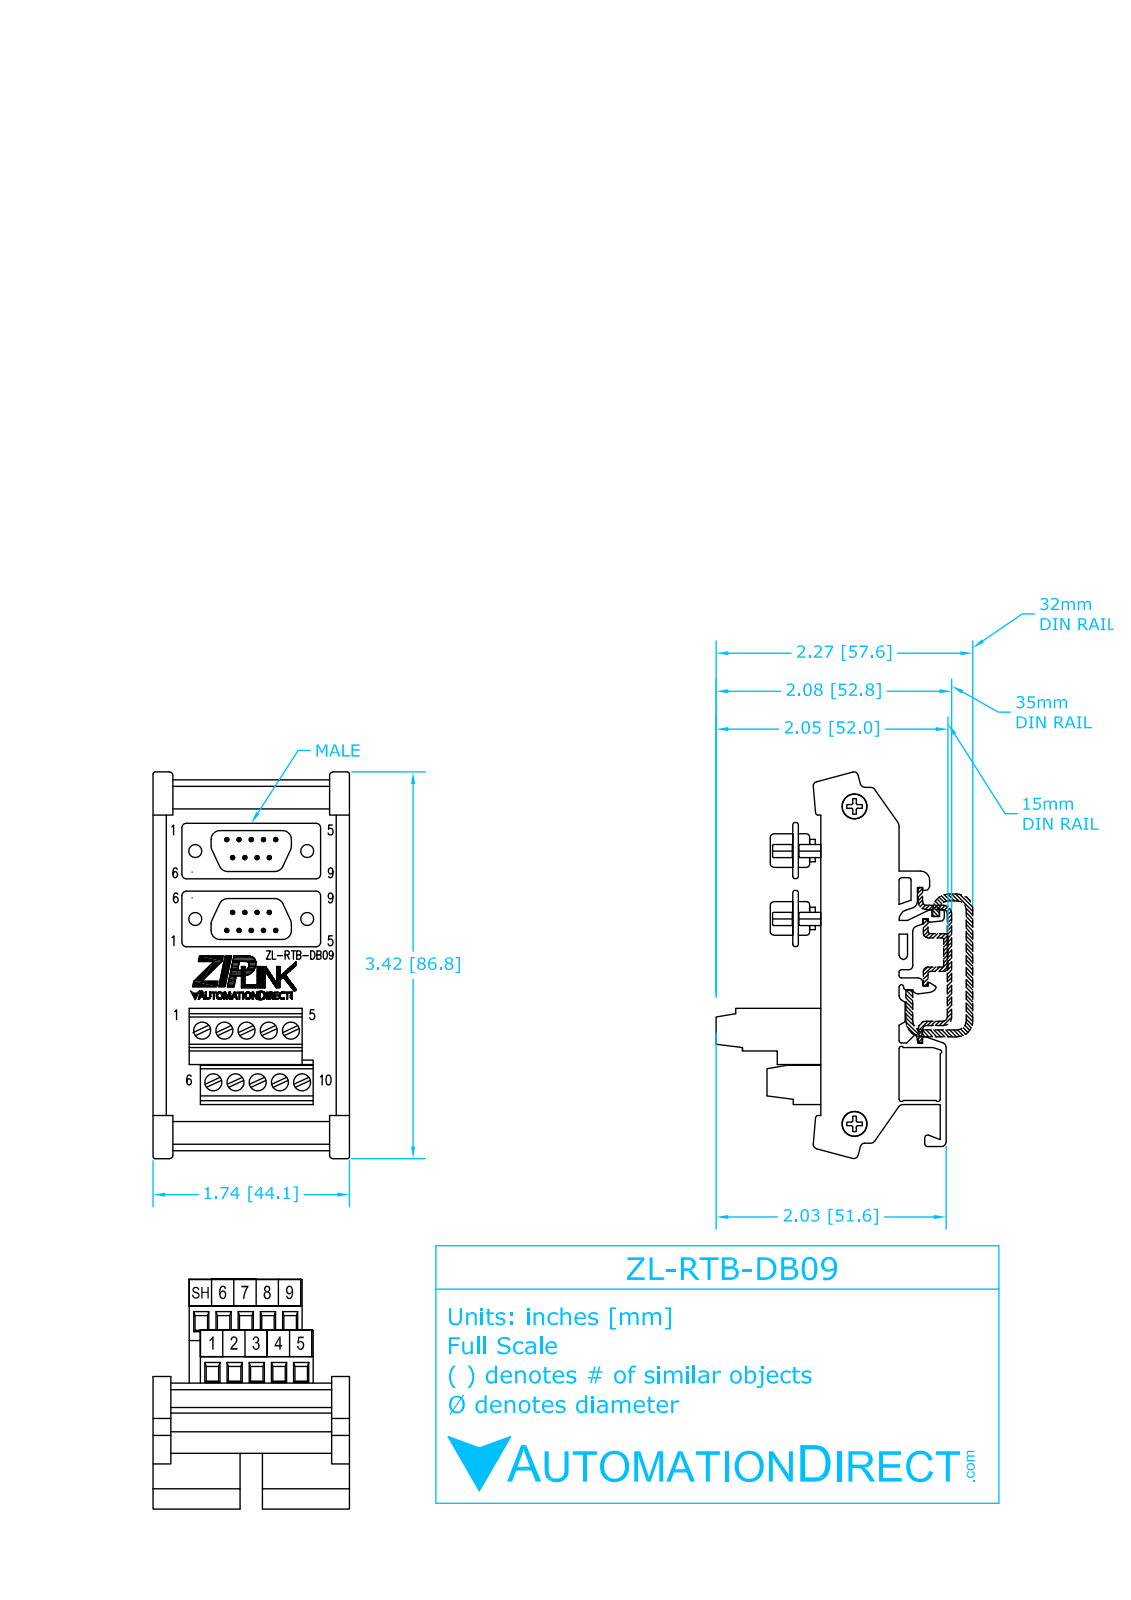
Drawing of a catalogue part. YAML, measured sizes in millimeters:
part_name: "ZL-RTB-DB09"
step_written_by: "SolidWorks 2014 (AUTOMOTIVE_DESIGN)"
units: millimeters
bodies: {solids: 1, faces: 786, planar: 557, cylindrical: 221, other: 8}
overall_size: [86.9, 51.6, 45.6]
volume: 75950
surface_area: 27730
round_holes:
  - {diameter: 3.8, count: 10}
  - {diameter: 1.4, count: 8}
  - {diameter: 2.3, count: 4}
  - {diameter: 5.7, count: 2}
  - {diameter: 1.4, count: 1}
round_bosses_or_shafts:
  - {diameter: 0.9, count: 8}
  - {diameter: 5.2, count: 2}
  - {diameter: 0.9, count: 1}
partial_cylinders:
  - {radius: 0.4, count: 41}
  - {radius: 0.8, count: 10}
  - {radius: 1.5, count: 8}
  - {radius: 2, count: 8}
  - {radius: 2.5, count: 8}
face_to_face_distances: [44.2, 0.8, 27.4, 28.2, 23.6, 0.9, 6.1, 10.7, 16.8, 17.5]
hole_center_spacings: [2.5, 5, 11.4, 3.2, 5.1, 10, 13.4, 3.3]
